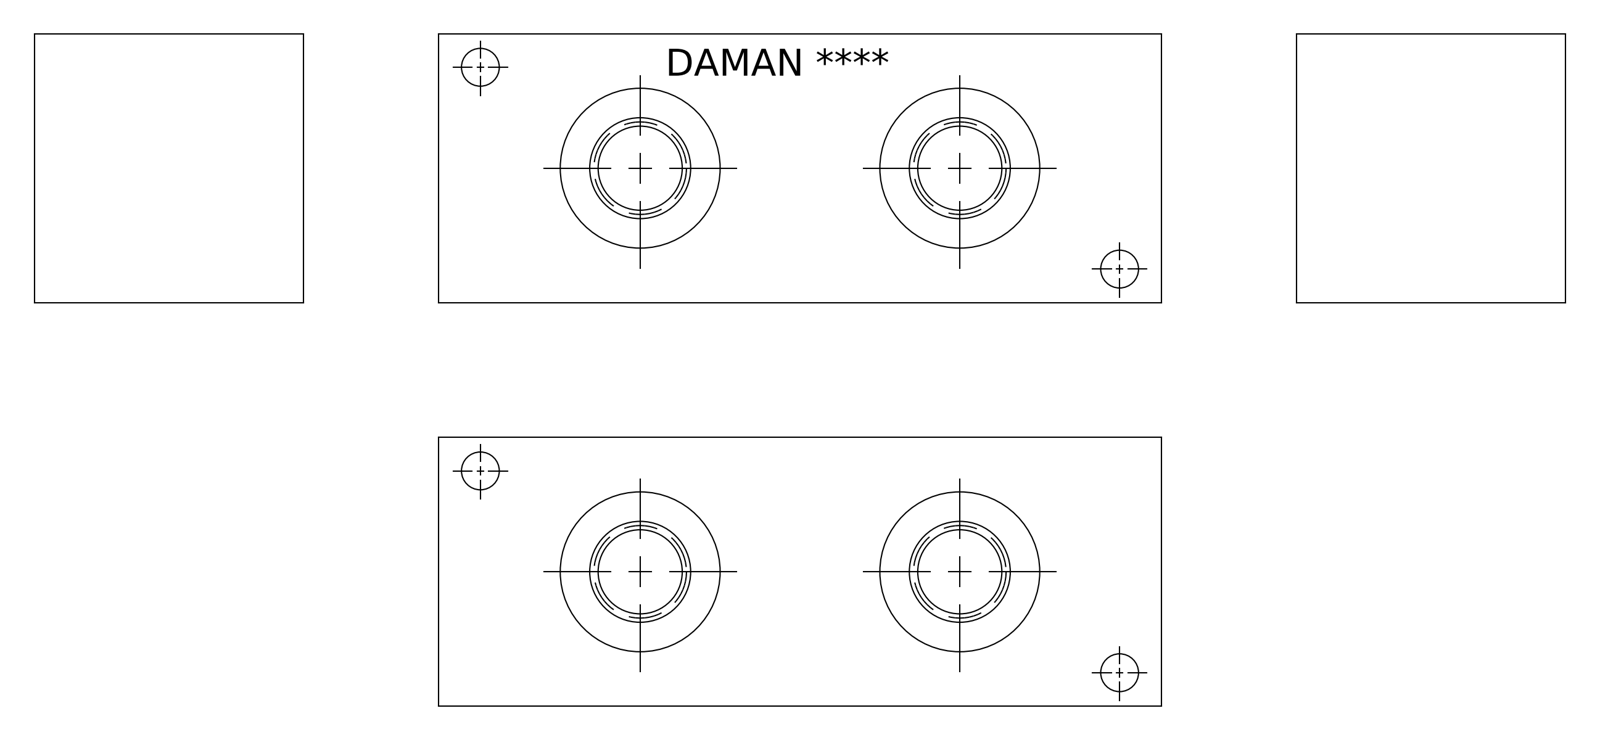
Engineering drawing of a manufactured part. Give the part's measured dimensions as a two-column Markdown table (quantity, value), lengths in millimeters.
| quantity | value |
| --- | --- |
| part name | Part_+J0900208S_3D |
| STEP written by | Autodesk Inventor 2020 (AUTOMOTIVE_DESIGN) |
| units | millimeters |
| bodies | 1 solid, 375 faces (205 planar, 28 cylindrical, 142 other) |
| overall size | 136.53 × 50.8 × 50.8 |
| volume | 318 711 mm³ |
| surface area | 41 281 mm² |
| round holes (diameter × count) | 7.14 × 4, 15.88 × 4, 17.5 × 4, 19.05 × 4, 19.25 × 4, 30.63 × 4 |
| main face-to-face distances | 50.8, 136.53, 50.01, 0.79, 35.74, 14.27, 15.06, 50.76, 0.75, 15.02 |
| hole center spacings | 35.69, 92.48, 60.32, 126.55 |
